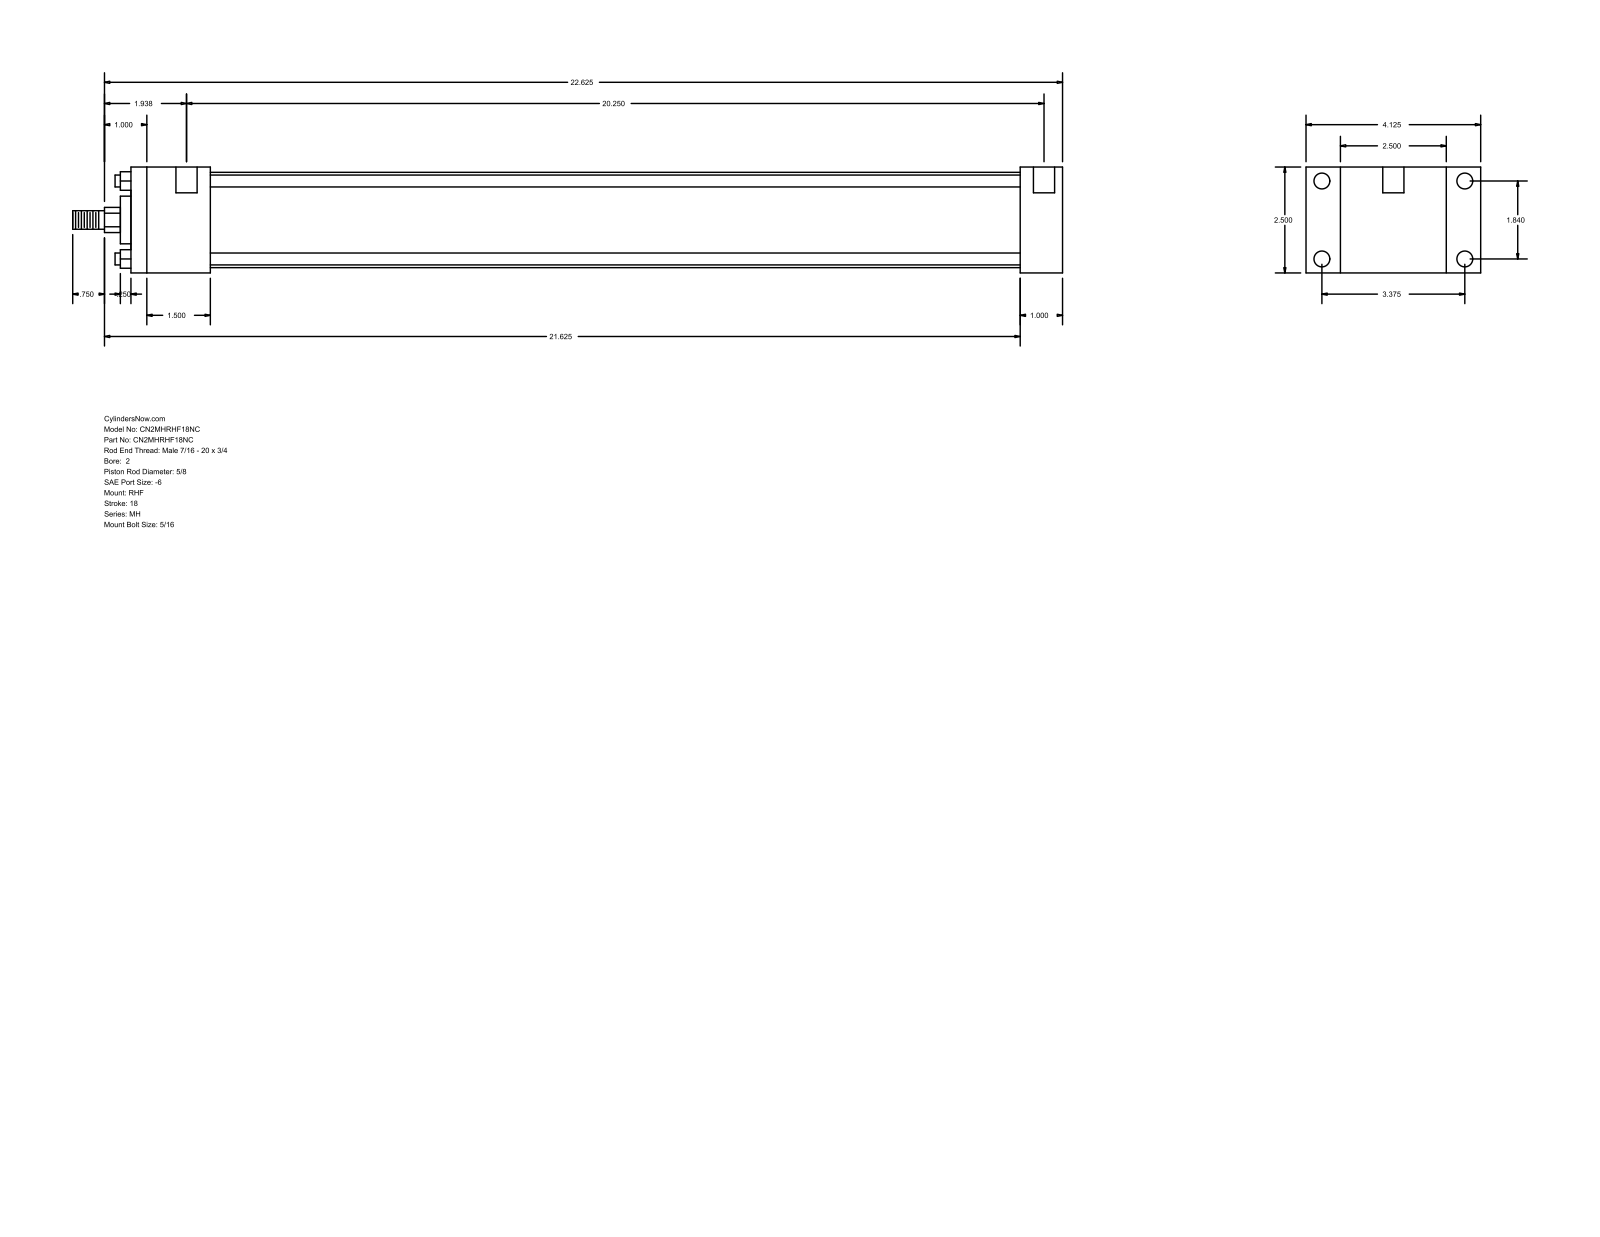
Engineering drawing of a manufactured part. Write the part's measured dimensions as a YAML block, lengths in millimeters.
part_name: "MH_RHF__0200_0.625"
step_written_by: "GSSL Pune (CONFIG_CONTROL_DESIGN)"
units: millimeters
bodies: {solids: 0, faces: 88, planar: 60, cylindrical: 28, other: 0}
overall_size: [593.73, 104.78, 63.5]
round_holes:
  - {diameter: 5.56, count: 4}
  - {diameter: 9.53, count: 4}
  - {diameter: 12.7, count: 2}
round_bosses_or_shafts:
  - {diameter: 7.14, count: 4}
  - {diameter: 57.15, count: 1}
  - {diameter: 28.57, count: 1}
  - {diameter: 15.88, count: 1}
  - {diameter: 11.11, count: 1}
partial_cylinders:
  - {radius: 7.54, count: 1}
face_to_face_distances: [63.5, 25.4, 20.64, 84.14, 533.39, 558.79, 104.78, 47.62, 485.77, 511.17]
hole_center_spacings: [46.74, 85.72, 97.63, 522.29, 3.18, 4.76, 514.35, 517.53]
